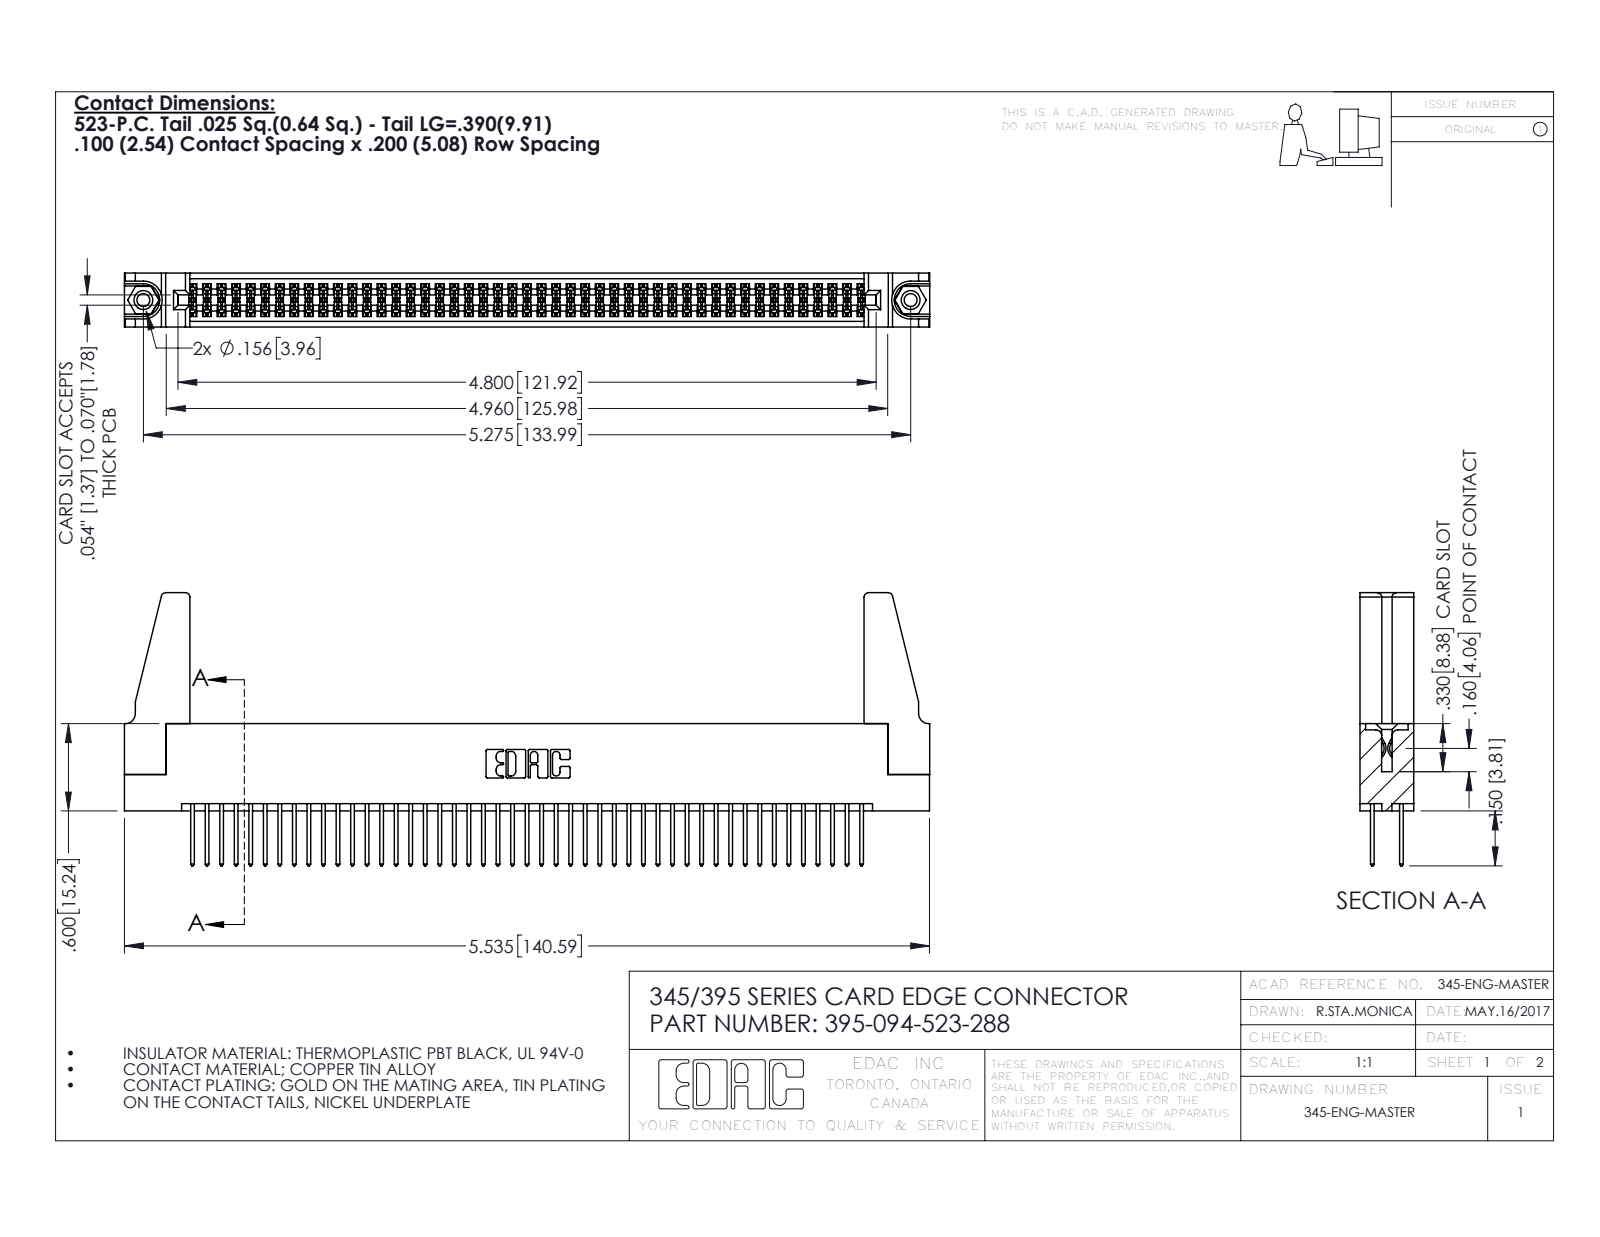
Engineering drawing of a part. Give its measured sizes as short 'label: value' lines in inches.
name: 345-292-001_345-293-123; 345 Part_Flush Mounting Lugs - 0.156 Dia-TH; 395-094-523-288; 345-250-001_345-250-001-102 (+1 more)
written by: SolidWorks 2016 (CONFIG_CONTROL_DESIGN)
unit: in
bodies: 99 solids, 4950 faces (3254 planar, 1680 cylindrical, 16 other)
size: 5.536 × 1.877 × 0.37
volume: 1.047 in³; area: 38.17 in²
holes: 2× ⌀0.089, 2× ⌀0.125, 2× ⌀0.156, 1× ⌀0.064
bosses: 2× ⌀0.155
rounds: 141× R0.006, 94× R0.01, 22× R0.01, 8× R0.03, 6× R0.007, 6× R0.031, 3× R0.026, 2× R0.014
face distances: 0.072, 0.298, 0.2, 0.37, 0.098, 0.272, 0.025, 0.225, 0.175, 0.149
hole spacings: 0.27, 5.039, 5.275
